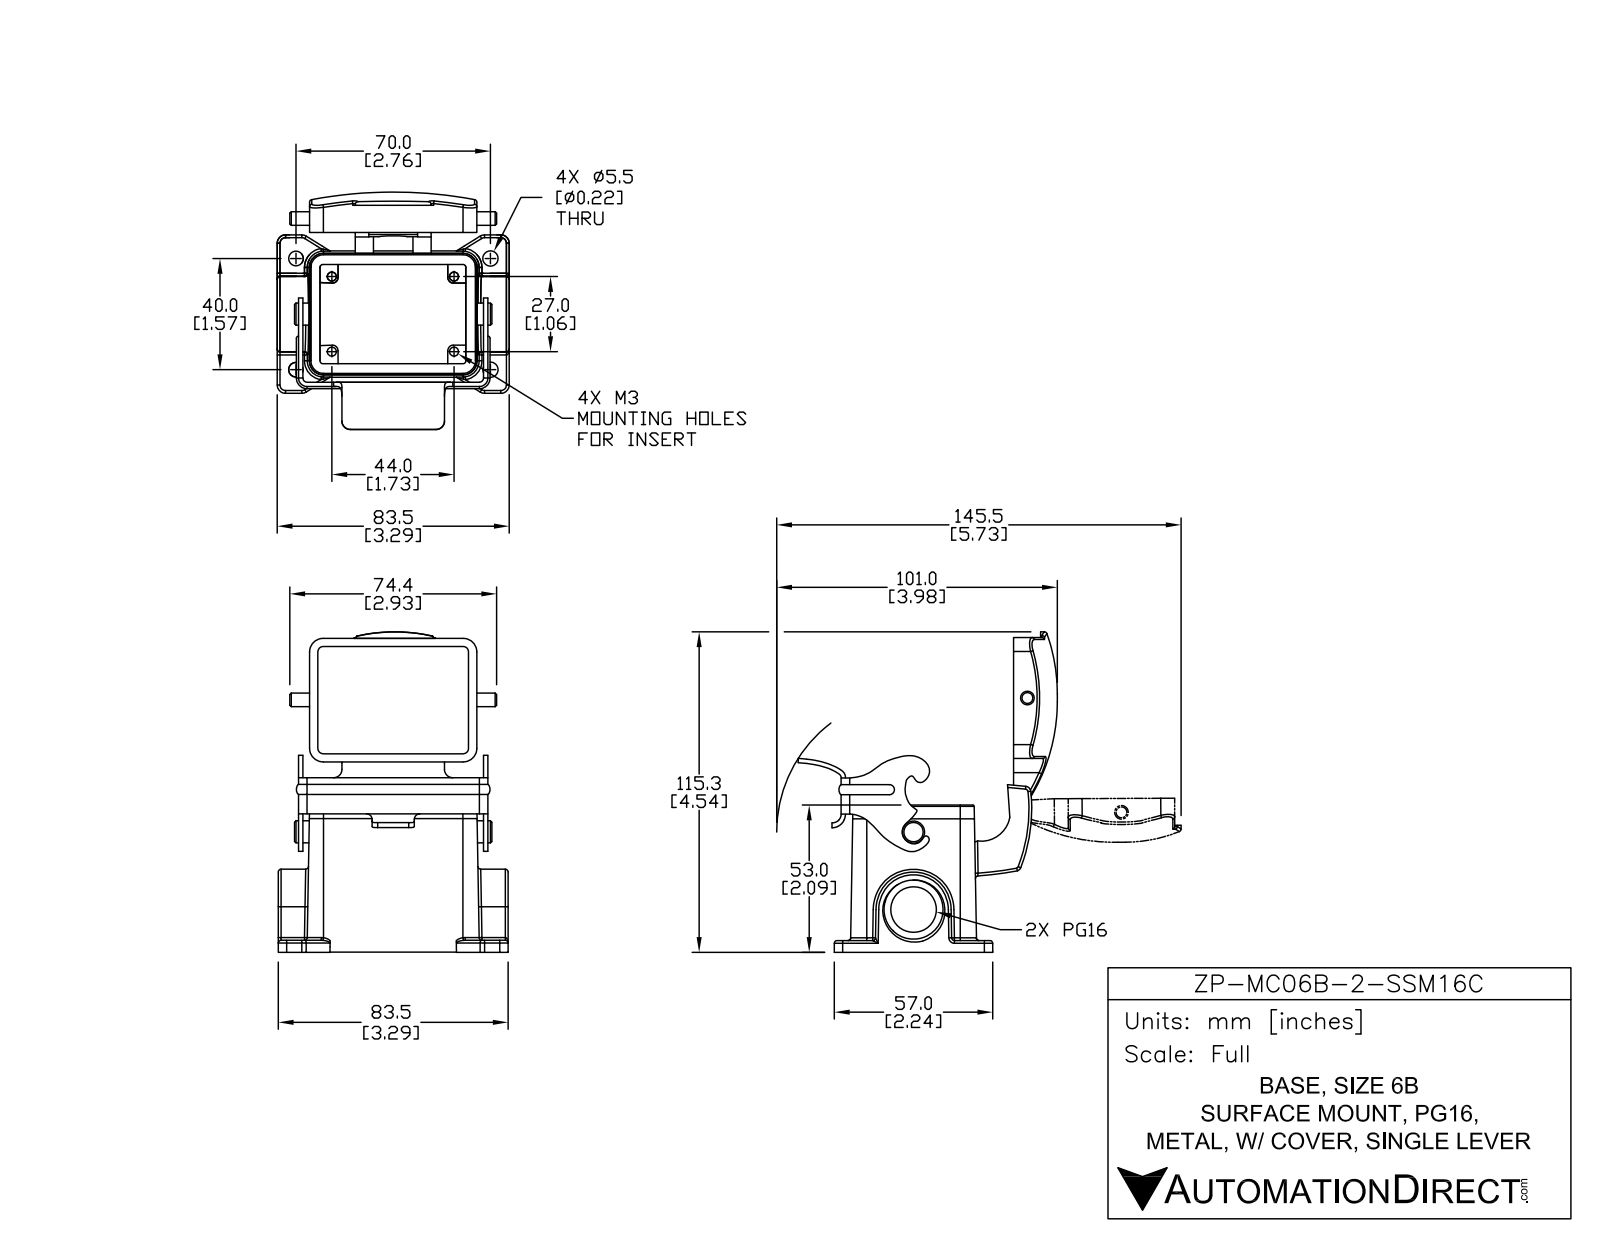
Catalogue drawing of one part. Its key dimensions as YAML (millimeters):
part_name: "ZP-MC06B-2-SSM16C"
step_written_by: "SolidWorks 2014 (AUTOMOTIVE_DESIGN)"
units: millimeters
bodies: {solids: 3, faces: 412, planar: 139, cylindrical: 158, other: 115}
overall_size: [114.53, 82.68, 81.2]
volume: 84013
surface_area: 49950
round_holes:
  - {diameter: 3, count: 4}
  - {diameter: 5.5, count: 4}
  - {diameter: 16.4, count: 1}
  - {diameter: 21.25, count: 1}
round_bosses_or_shafts:
  - {diameter: 7.95, count: 1}
  - {diameter: 4.9, count: 1}
partial_cylinders:
  - {radius: 1, count: 27}
  - {radius: 2, count: 14}
  - {radius: 3, count: 12}
  - {radius: 5, count: 6}
  - {radius: 0.5, count: 4}
  - {radius: 1.5, count: 2}
  - {radius: 3.06, count: 2}
  - {radius: 8, count: 2}
face_to_face_distances: [3.95, 1.56, 4.03, 3, 66.56, 40.48, 14.06, 54.06, 12.5, 52.5]
hole_center_spacings: [14.53, 35.93, 57.37, 66.12, 27, 40, 44, 51.62]
